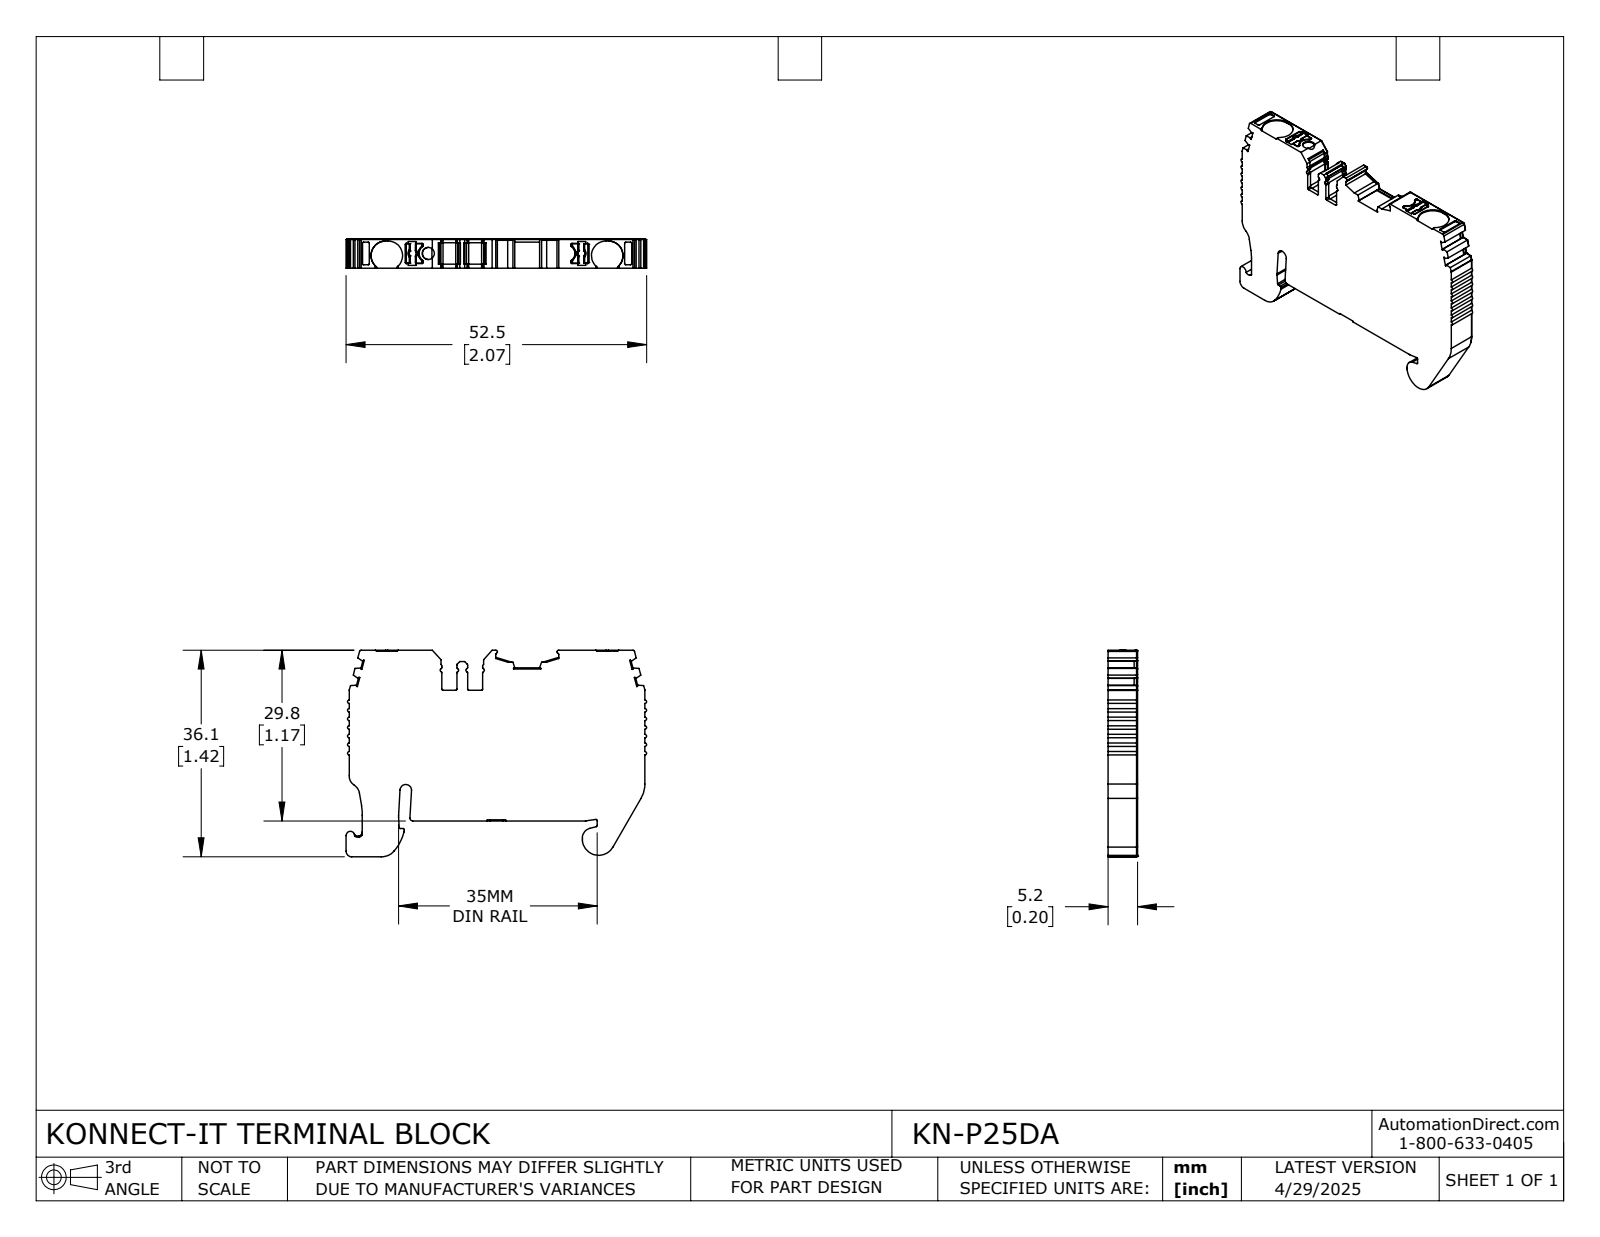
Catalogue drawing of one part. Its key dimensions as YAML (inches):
part_name: "KN-P25DA"
step_written_by: "SolidWorks 2024 (CONFIG_CONTROL_DESIGN)"
units: inches
bodies: {solids: 1, faces: 584, planar: 308, cylindrical: 239, other: 37}
overall_size: [2.066, 1.42, 0.203]
volume: 0.468
surface_area: 6.63
round_holes:
  - {diameter: 0.083, count: 1}
partial_cylinders:
  - {radius: 0.008, count: 54}
  - {radius: 0.012, count: 39}
  - {radius: 0.02, count: 18}
  - {radius: 0.004, count: 17}
  - {radius: 0.016, count: 9}
  - {radius: 0.006, count: 8}
  - {radius: 0.1, count: 4}
  - {radius: 0.039, count: 3}
face_to_face_distances: [0.203, 1.166, 1.174, 2.033, 0.177, 0.197, 0.246, 1.412, 0.079, 1.42]
